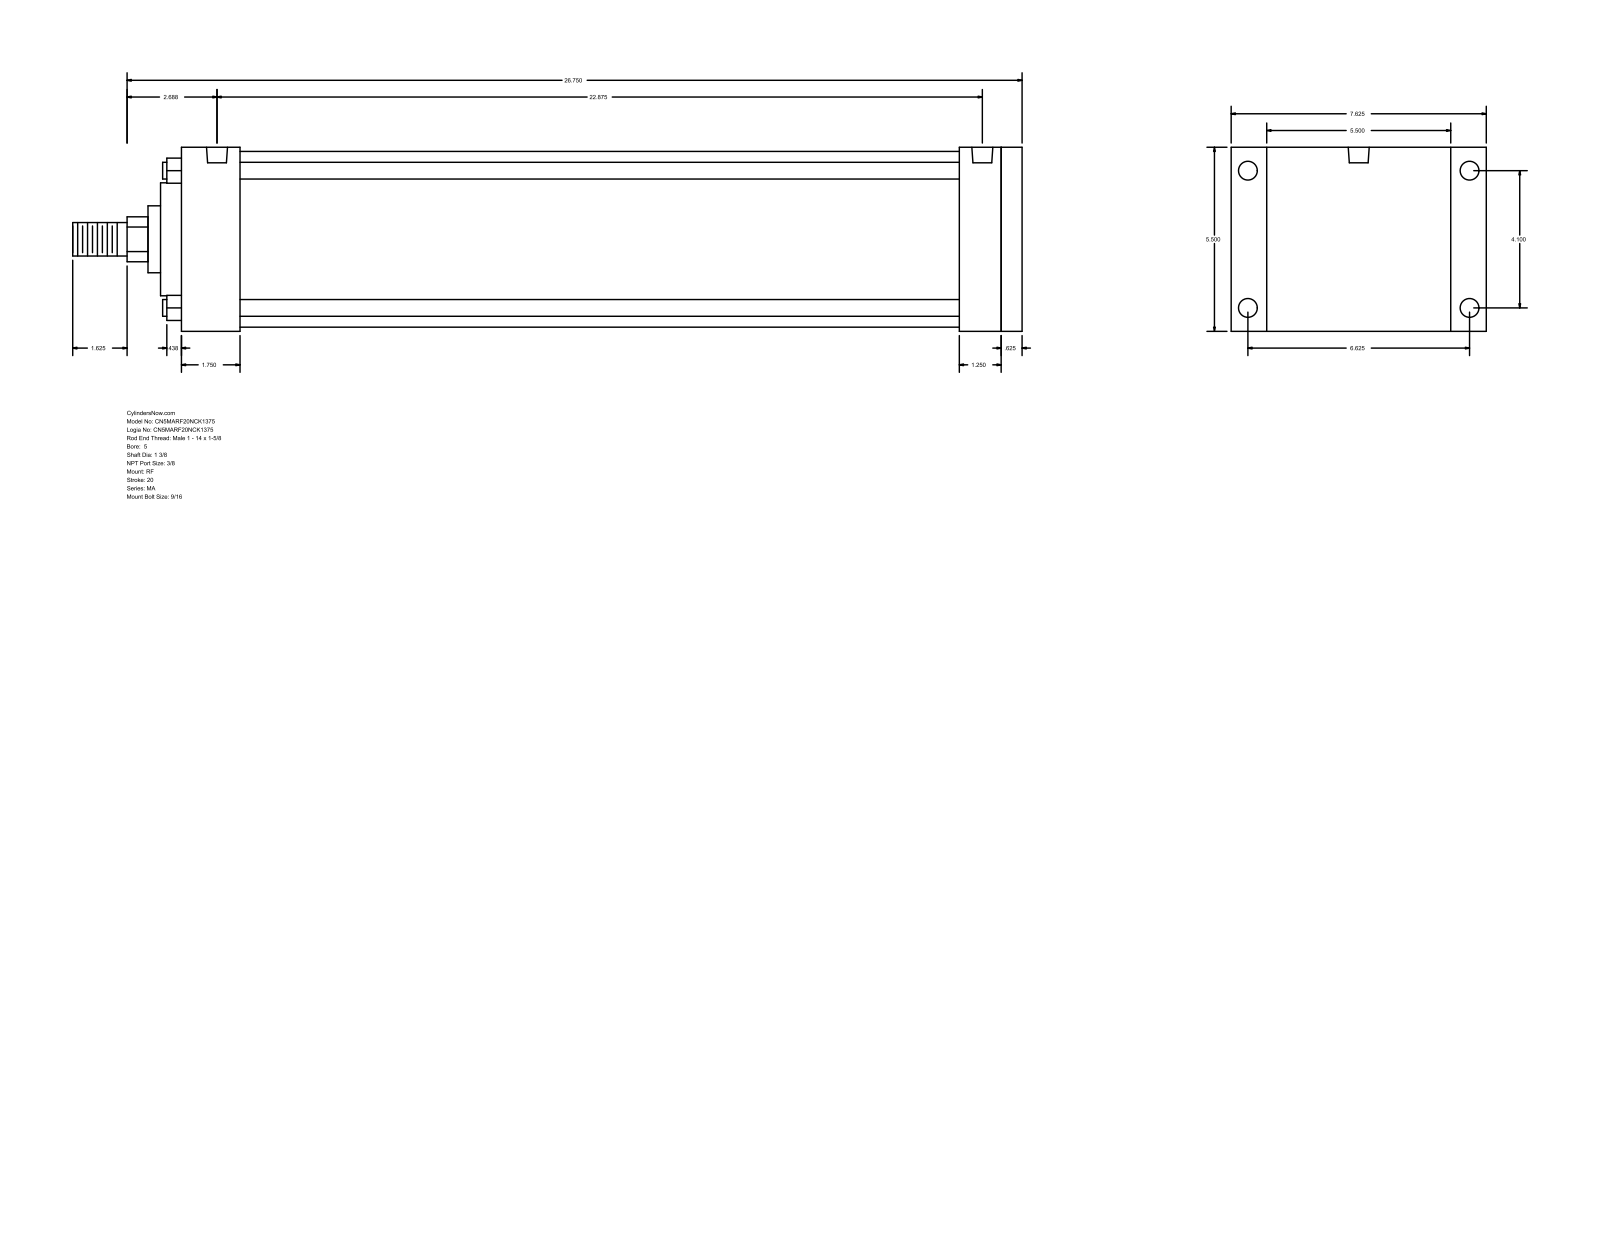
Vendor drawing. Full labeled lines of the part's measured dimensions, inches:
Part name (STEP PRODUCT): MA_RF__0500_1.375
STEP written by: GSSL Pune (CONFIG_CONTROL_DESIGN)
Units: inches
Bodies: 0 solids, 94 faces (65 planar, 29 cylindrical, 0 other)
Overall size (bounding box): 28.375 × 7.625 × 5.5
Round holes (diameter × count): ⌀0.437 ×4, ⌀0.563 ×4, ⌀0.627 ×2
Round bosses / shafts (diameter × count): ⌀0.5 ×4, ⌀5.25 ×1, ⌀3.375 ×1, ⌀2 ×1, ⌀1.375 ×1, ⌀1 ×1
Partial cylindrical surfaces — rounded edges, fillets, slot ends (radius × count): R0.672 ×1
Main face-to-face distances: 5.5, 25.125, 0.625, 24.5, 1.75, 22.75, 23.375, 23.25, 21.5, 1.25
Hole centre spacings: 0.188, 4.1, 6.625, 7.791, 22.5, 22.687, 22.875
